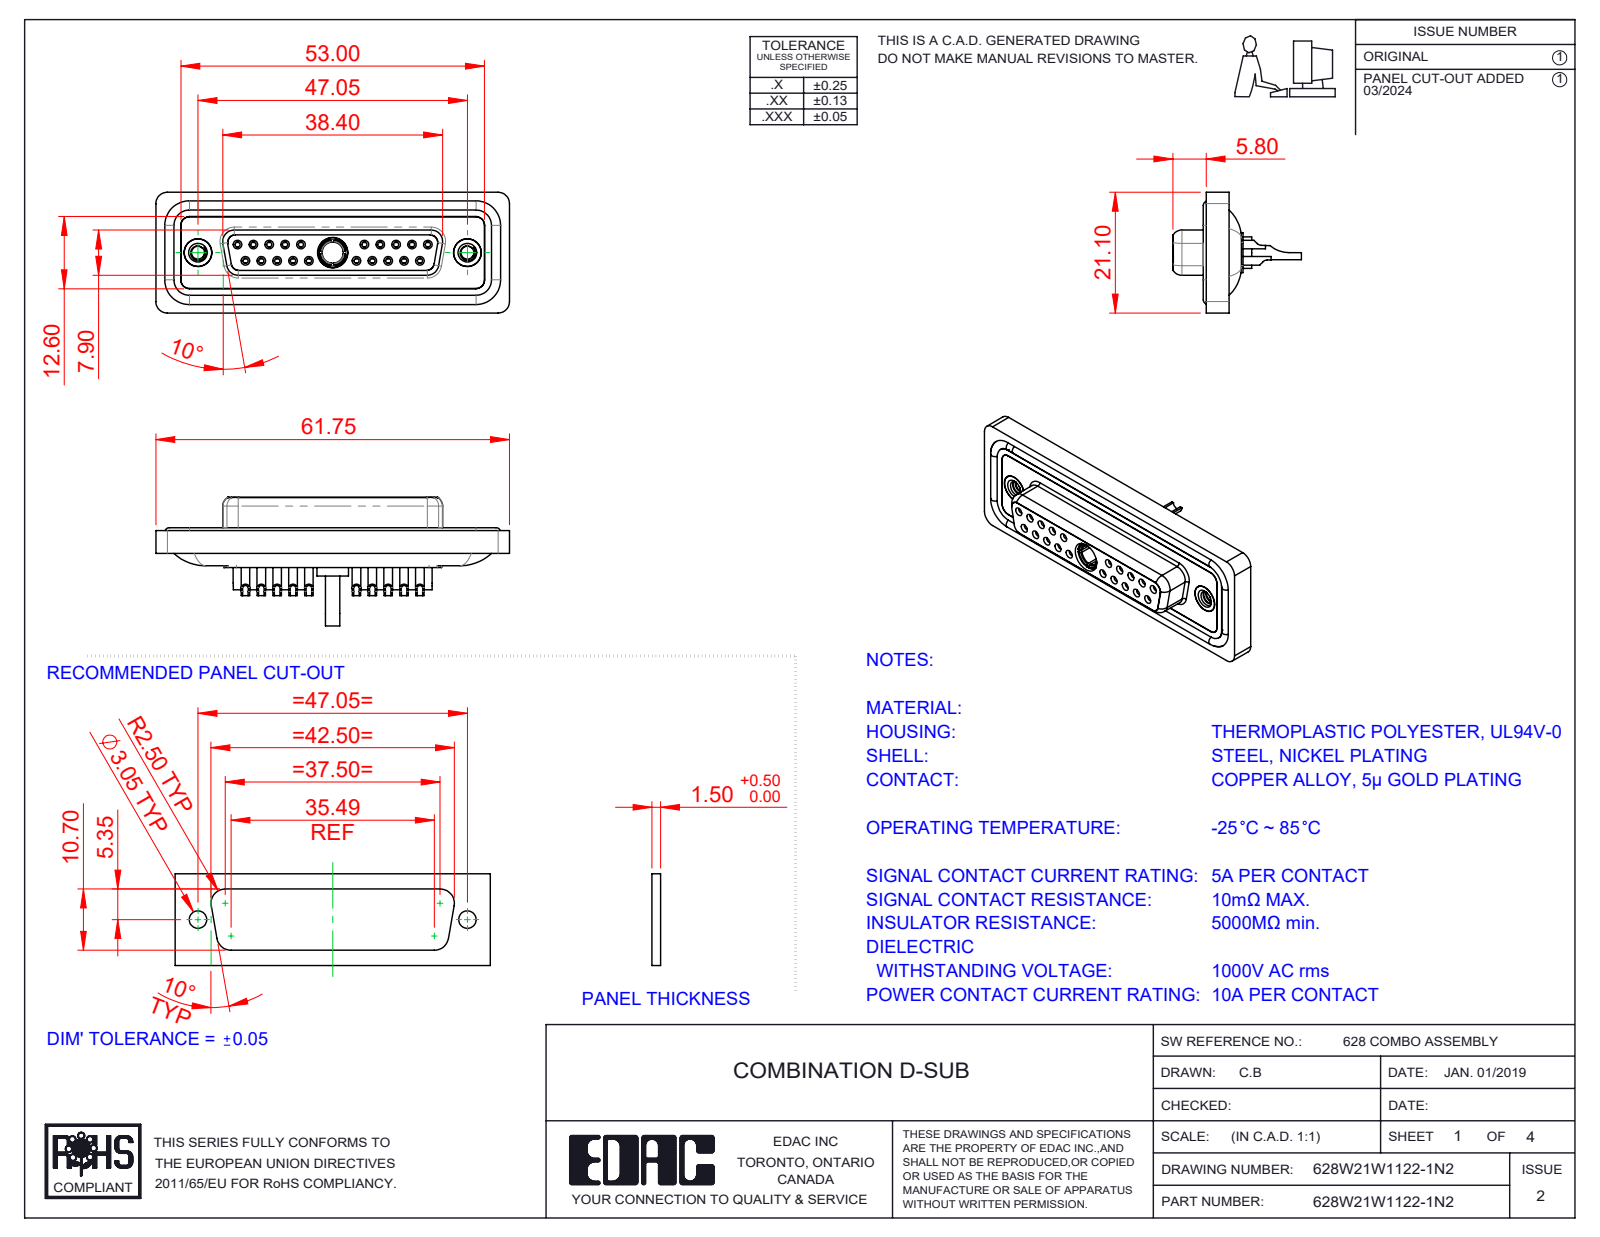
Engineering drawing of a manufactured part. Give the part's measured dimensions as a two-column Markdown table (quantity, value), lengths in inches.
| quantity | value |
| --- | --- |
| part name | 628Combo Housing_21W1; 628Combo Contact Row 1_22; Power Socket_10A SC; 628Combo Contact Row 2_22 (+5 more) |
| STEP written by | SolidWorks 2023 (CONFIG_CONTROL_DESIGN) |
| units | inches |
| bodies | 29 solids, 1565 faces (476 planar, 634 cylindrical, 455 other) |
| overall size | 2.431 × 0.884 × 0.831 |
| volume | 0.513 in³ |
| surface area | 22.1 in² |
| round holes (diameter × count) | 0.035 × 20, 0.039 × 20, 0.043 × 20, 0.059 × 20, 0.079 × 20, 0.063 × 10, 0.067 × 10, 0.191 × 3, 0.089 × 2, 0.157 × 2, 0.159 × 2, 0.197 × 2 |
| round bosses / shafts (diameter × count) | 0.087 × 20, 0.063 × 14, 0.195 × 2, 0.189 × 2, 0.217 × 1, 0.205 × 1, 0.195 × 1, 0.187 × 1 |
| partial cylindrical surfaces (radius × count) | 0.059 × 22, 0.079 × 18, 0.053 × 8, 0.063 × 8, 0.039 × 6, 0.01 × 4, 0.02 × 4, 0.024 × 4 |
| main face-to-face distances | 0.016, 0.071, 0.293, 0.222, 0.26, 0.02, 0.063, 0.278, 0.114, 0.043 |
| hole center spacings | 0.124, 0.109, 0.218, 0.198, 0.327, 0.294, 0.654, 0.763 |
